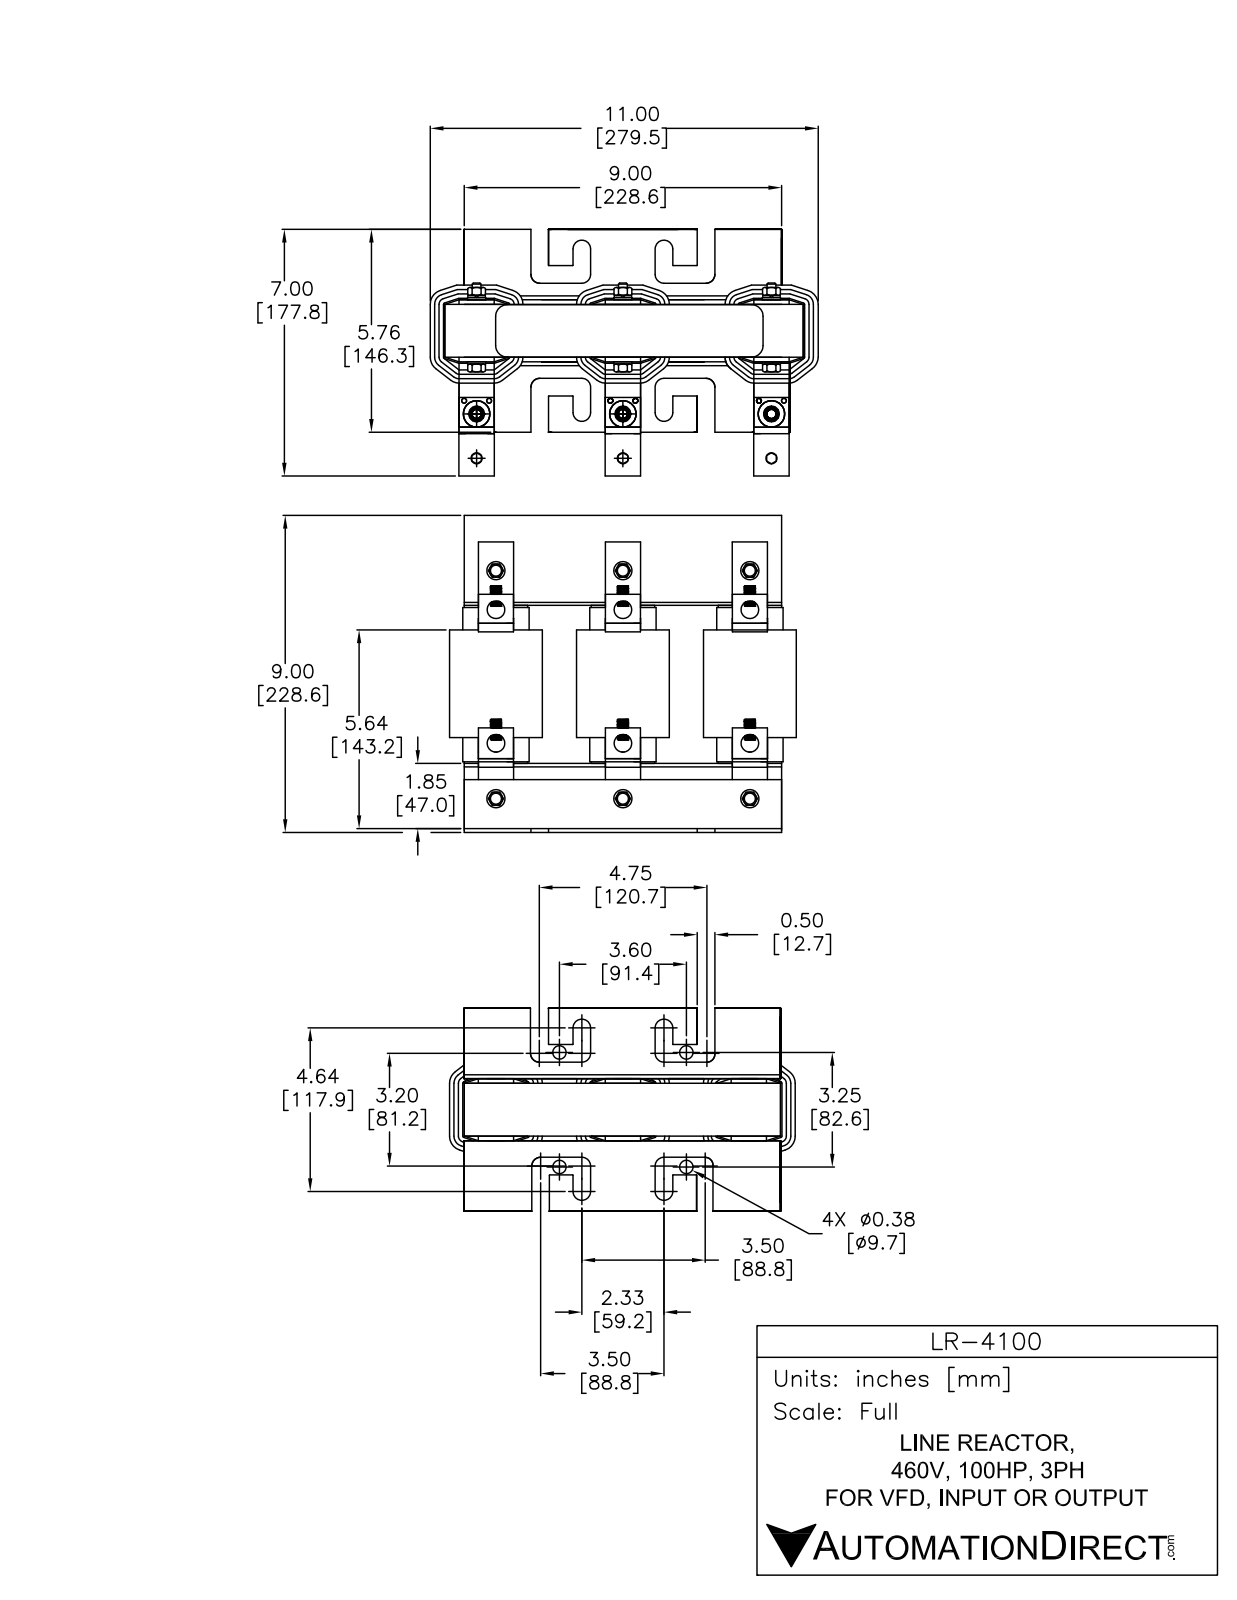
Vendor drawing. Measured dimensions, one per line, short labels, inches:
name: LR-4100
written by: SolidWorks 2011 (AUTOMOTIVE_DESIGN)
unit: in
bodies: 53 solids, 927 faces (675 planar, 252 cylindrical, 0 other)
size: 10.224 × 8.252 × 6.94
volume: 199.9 in³; area: 1 213 in²
holes: 9× ⌀0.63, 6× ⌀0.138, 3× ⌀0.615
bosses: 8× ⌀0.246, 6× ⌀0.748, 6× ⌀0.515, 6× ⌀0.465
rounds: 24× R0.415, 18× R0.257, 12× R0.1, 12× R0.218, 12× R0.25, 12× R0.375, 12× R0.612, 8× R0.01
face distances: 1.5, 3.6, 0.14, 1.64, 1.84, 0.03, 0.17, 1.67, 1.81, 0.157
hole spacings: 3.6, 7.2, 3.605, 5.24, 0.194, 0.709, 3.807, 2.891
